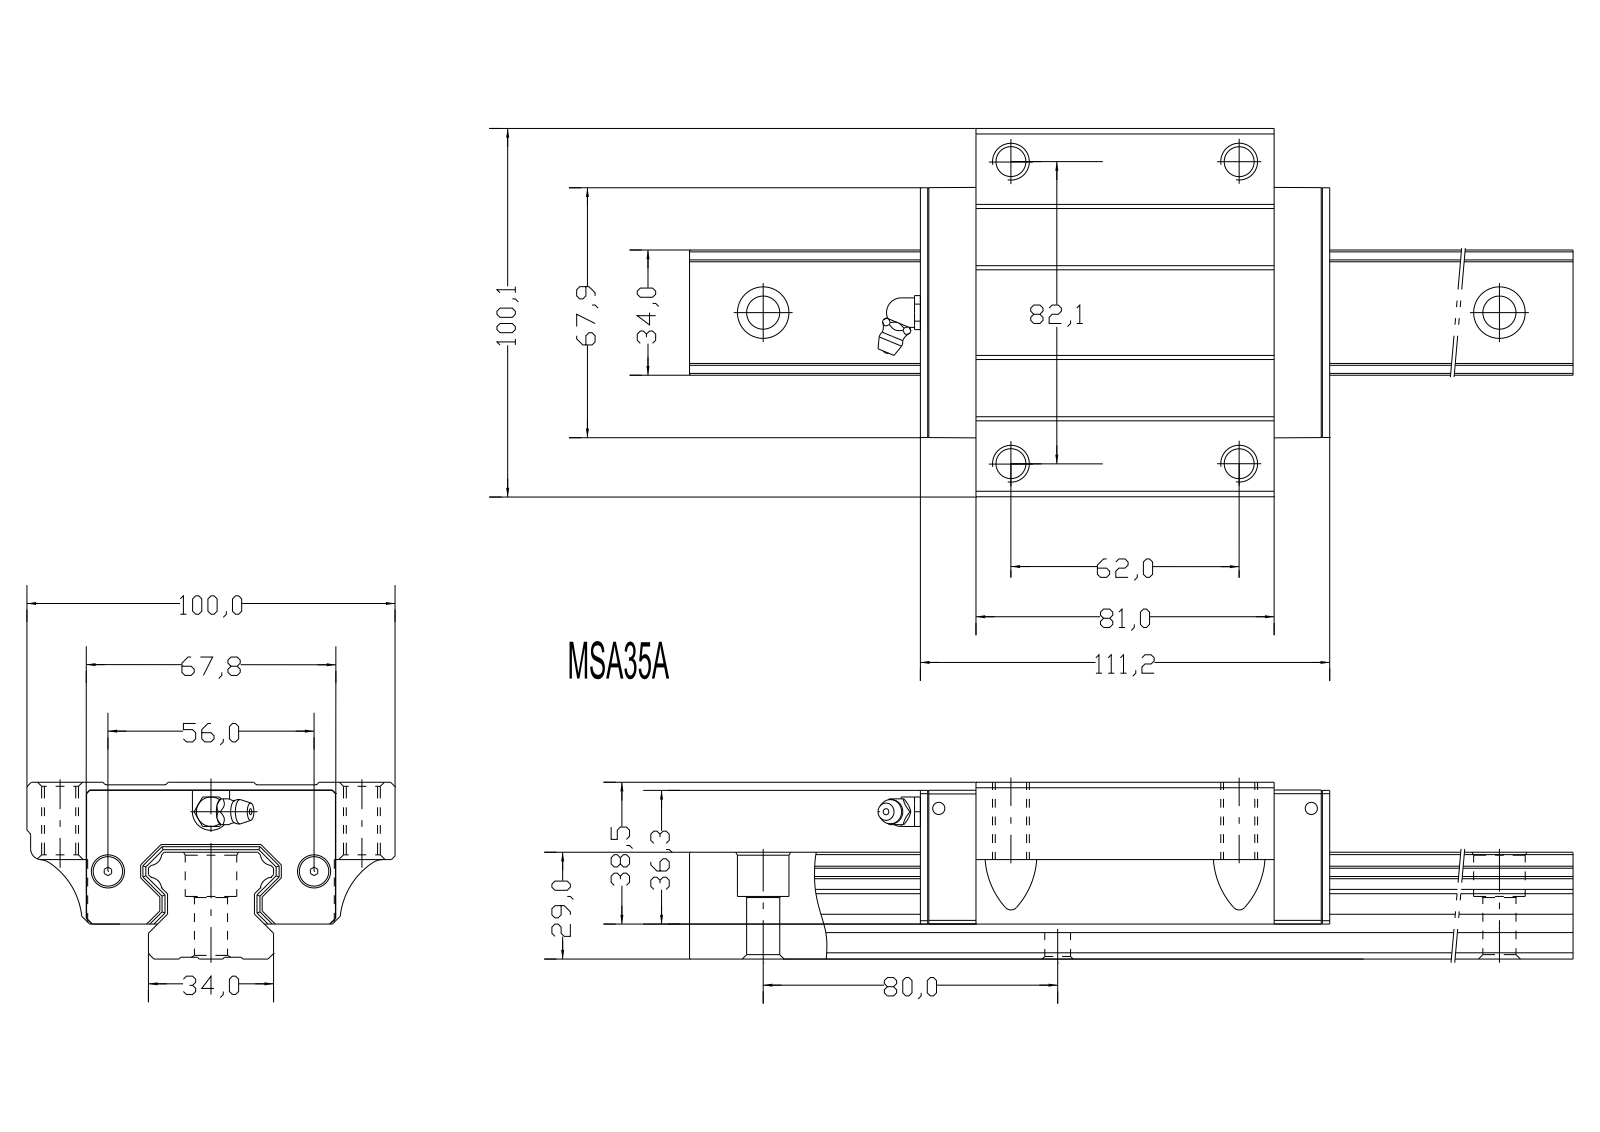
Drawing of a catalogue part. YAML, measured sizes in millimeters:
step_written_by: "Kubotek KeyCreator V6.5.2 (0407) (CONFIG_CONTROL_DESIGN)"
units: millimeters
bodies: {solids: 3, faces: 234, planar: 145, cylindrical: 72, other: 17}
overall_size: [280, 100, 48]
volume: 500603
surface_area: 83456
round_holes:
  - {diameter: 9, count: 6}
  - {diameter: 10, count: 4}
  - {diameter: 14, count: 4}
  - {diameter: 4.5, count: 2}
round_bosses_or_shafts:
  - {diameter: 8, count: 1}
partial_cylinders:
  - {radius: 3.5, count: 4}
  - {radius: 7, count: 4}
  - {radius: 5, count: 2}
  - {radius: 20, count: 2}
  - {radius: 1, count: 1}
  - {radius: 3, count: 1}
  - {radius: 5.05, count: 1}
face_to_face_distances: [29, 0.7, 47.3, 19, 48, 9.5, 19.5, 38.5, 16.8, 5.3]
hole_center_spacings: [41.98, 81.99, 97.99, 156.47, 80, 62, 82, 102.8]
